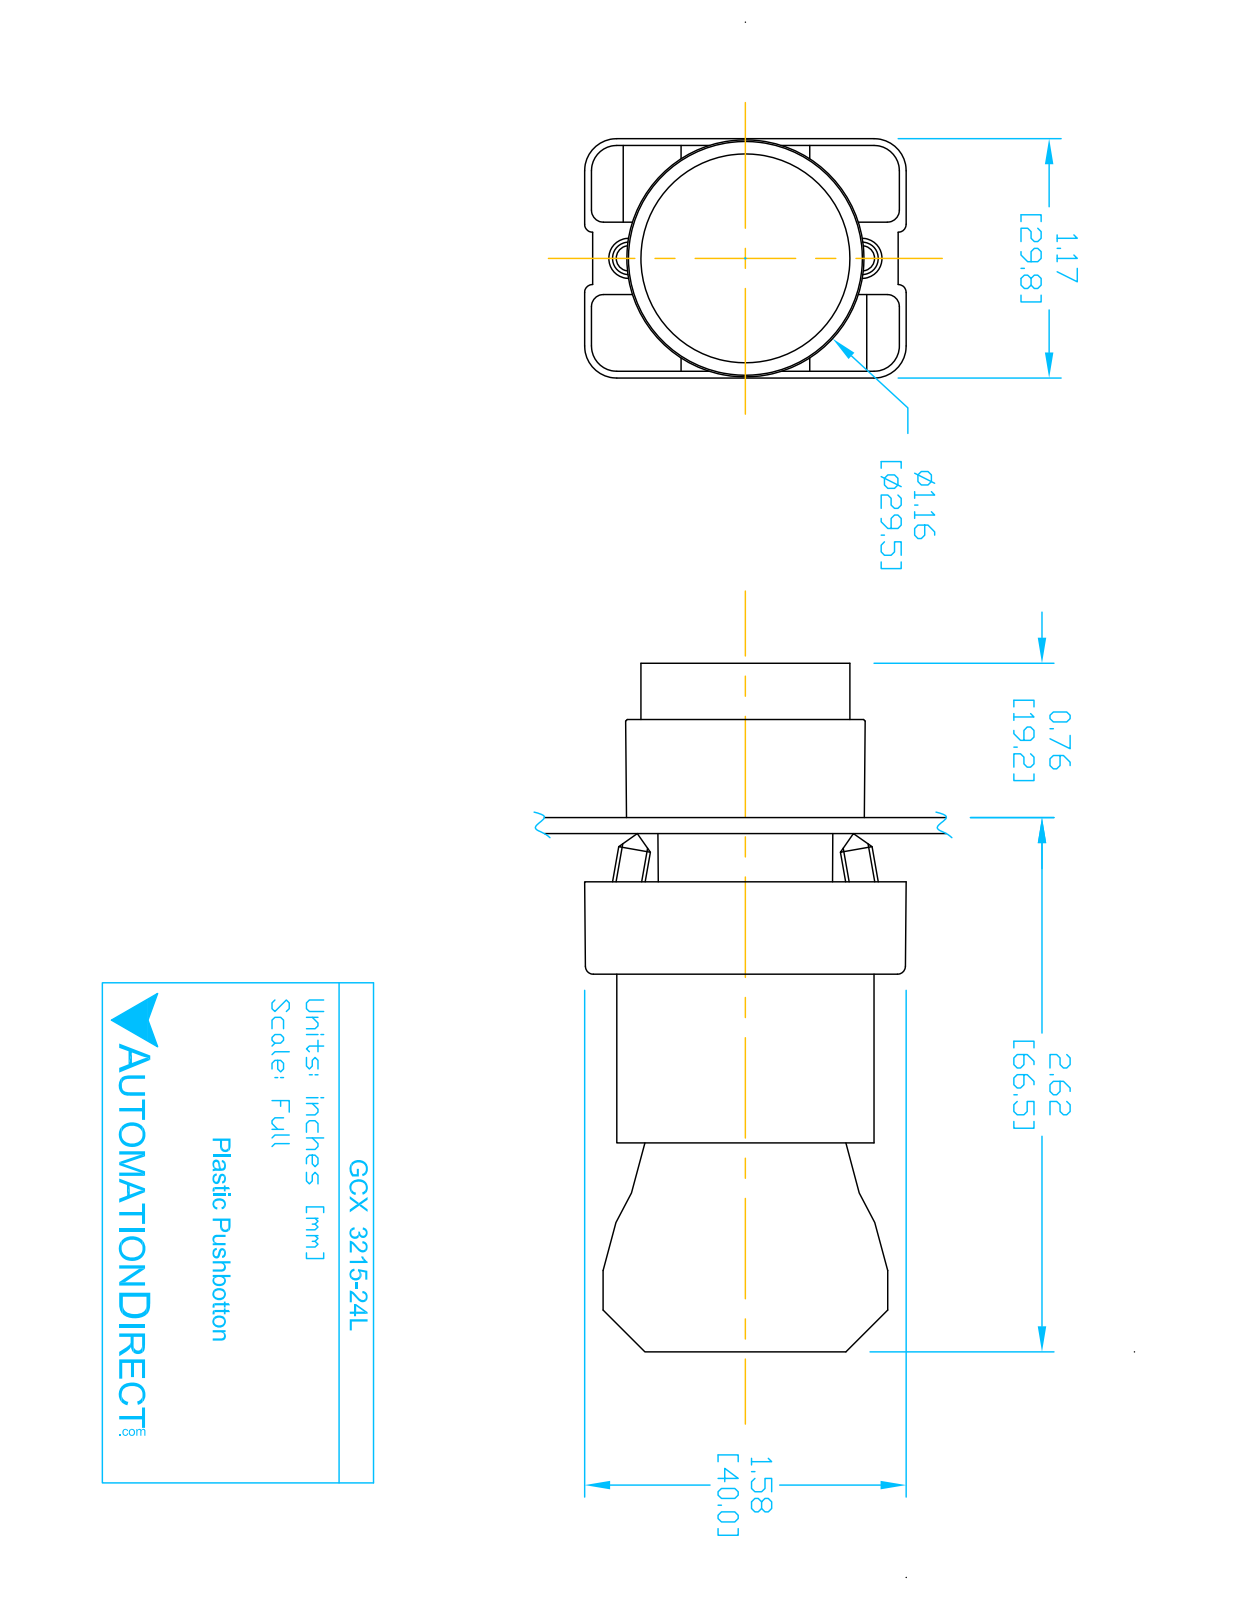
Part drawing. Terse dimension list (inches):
name: ECX1050; GCX3215-24L; GCX3215L OPERATOR; ecx1040 (+1 more)
written by: SolidWorks 2016 (AUTOMOTIVE_DESIGN)
unit: in
bodies: 7 solids, 425 faces (250 planar, 144 cylindrical, 31 other)
size: 3.319 × 1.581 × 1.177
volume: 2.721 in³; area: 36.32 in²
holes: 2× ⌀0.079, 2× ⌀0.124, 2× ⌀0.13, 1× ⌀0.087, 1× ⌀0.197, 1× ⌀0.469, 1× ⌀0.878, 1× ⌀0.888, 1× ⌀1.024
bosses: 4× ⌀0.157, 1× ⌀1.175, 1× ⌀1.004, 1× ⌀0.945, 1× ⌀0.856, 1× ⌀0.78, 1× ⌀0.504
rounds: 24× R0.059, 12× R0.041, 12× R0.124, 12× R0.157, 8× R0.039, 2× R0.128, 1× R0.02, 1× R0.063
face distances: 0.827, 0.579, 1.171, 2.02, 1.193, 0.031, 0.033, 0.573, 1.165, 0.593
hole spacings: 0.236, 0.544, 0.472, 0.49
